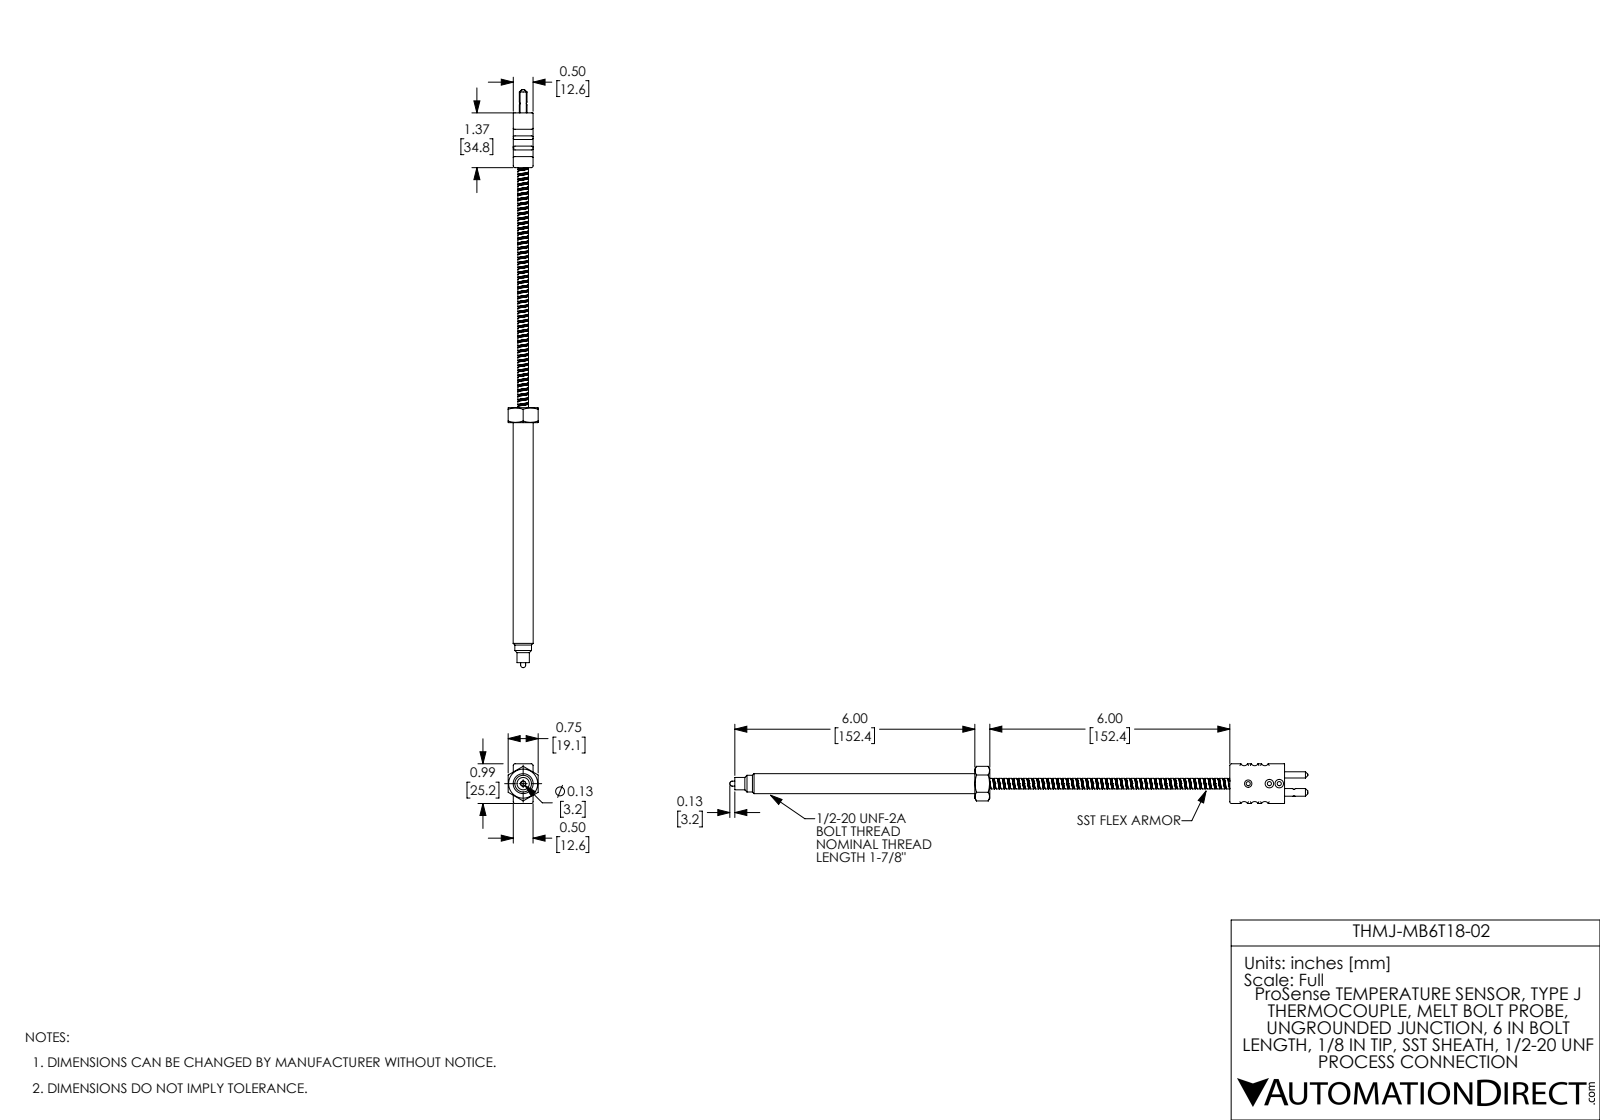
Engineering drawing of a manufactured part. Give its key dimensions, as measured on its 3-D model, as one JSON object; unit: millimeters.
{"part_name": "THMJ-MB6T18-02", "step_written_by": "SolidWorks 2017 (AUTOMOTIVE_DESIGN)", "units": "millimeters", "bodies": {"solids": 3, "faces": 312, "planar": 69, "cylindrical": 172, "other": 71}, "overall_size": [367.1, 25.2, 19.1], "volume_mm3": 37250, "surface_area_mm2": 15400, "round_holes": [[2.6, 2], [4, 2], [3.4, 1], [4.7, 1], [7.5, 1], [7.8, 1]], "round_bosses_or_shafts": [[12.7, 1], [10.6, 1], [7.8, 1], [7.1, 1], [6.7, 1], [4.9, 1], [4, 1], [3.2, 1]], "partial_cylinders_radius": [[1.1, 8], [2.4, 6], [0.3, 4]], "face_to_face_distances": [12.6, 19.1, 187.2, 152.4, 25.2, 3.2, 15.8, 34.8, 161.9, 196.7], "hole_center_spacings": [5.5, 8.3, 14.5, 6.3, 11, 13.4, 19.7]}
